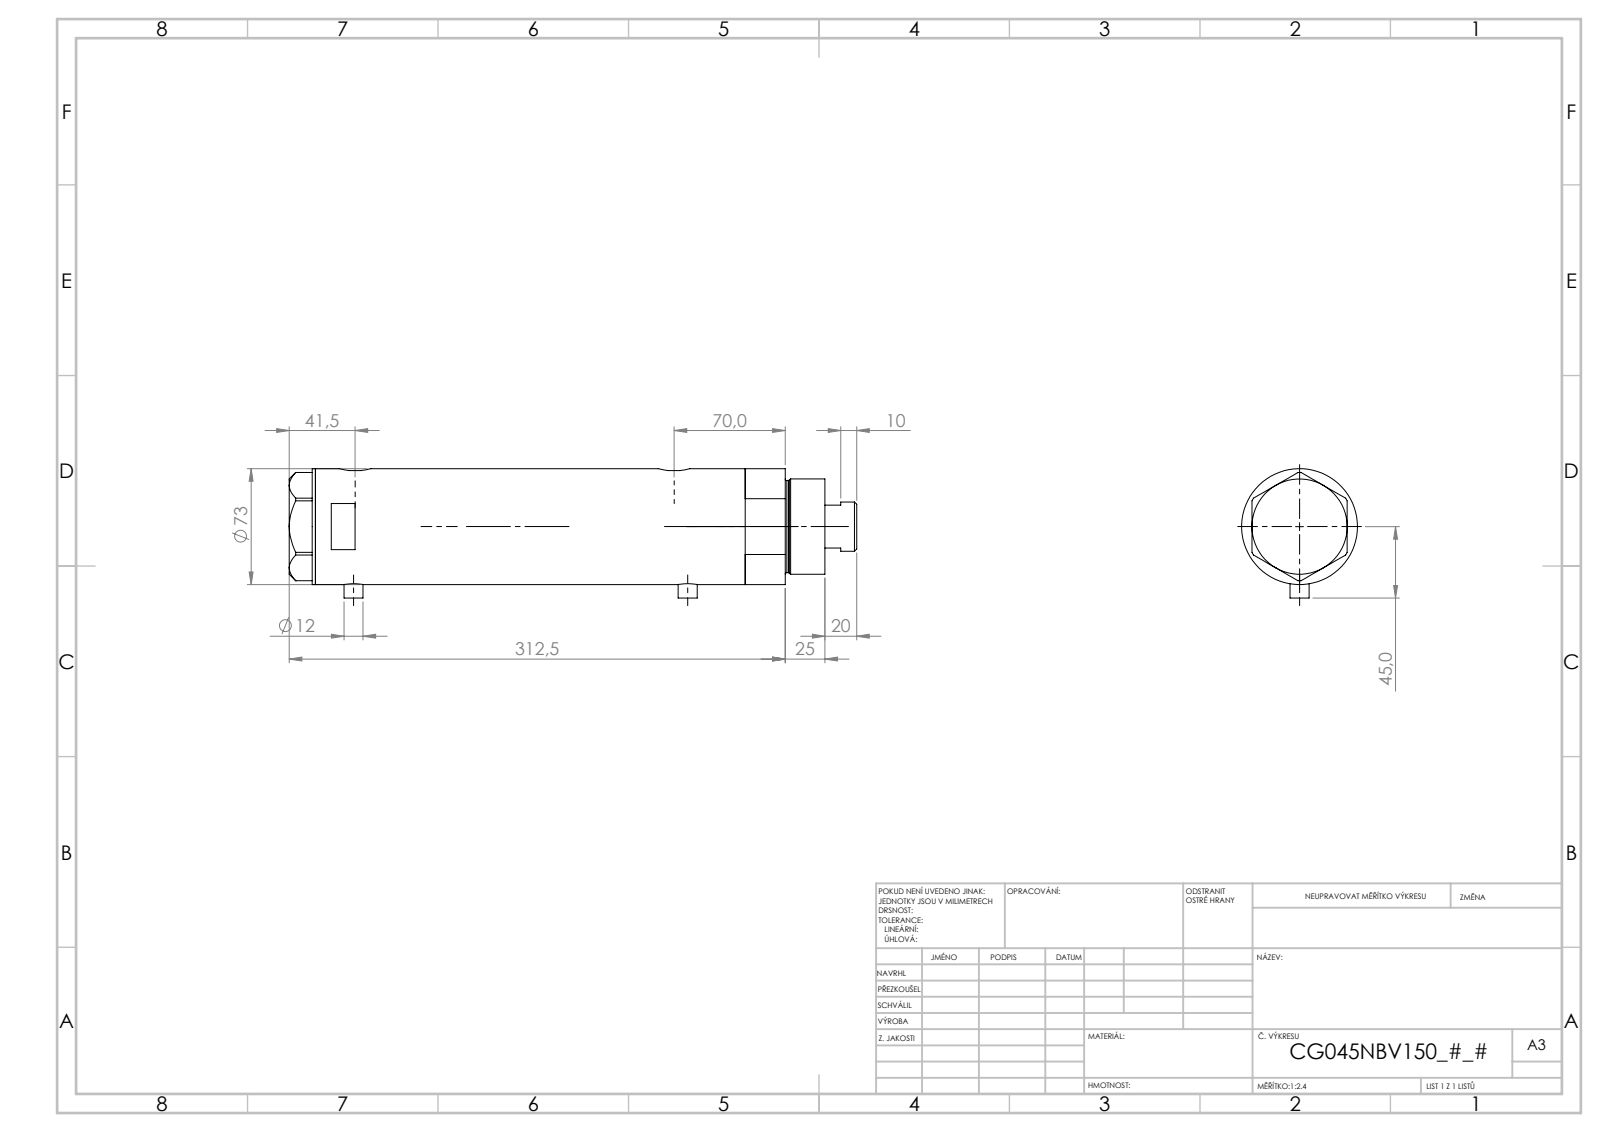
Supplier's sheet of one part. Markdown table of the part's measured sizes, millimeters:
| quantity | value |
| --- | --- |
| part name | V270CG_BACK; V270CG_VC; V270CG_FRONT; V270CG_MIDDLE |
| STEP written by | SolidWorks 2019 (CONFIG_CONTROL_DESIGN) |
| units | millimeters |
| bodies | 4 solids, 120 faces (49 planar, 51 cylindrical, 20 other) |
| overall size | 357.5 × 81.5 × 73 |
| volume | 1 247 000 mm³ |
| surface area | 198 635 mm² |
| round holes (diameter × count) | 12.5 × 2, 13.16 × 2, 10.5 × 1, 32 × 1, 33.5 × 1, 45 × 1, 48 × 1, 64 × 1 |
| round bosses / shafts (diameter × count) | 12 × 2, 73 × 1, 60 × 1, 58 × 1, 31 × 1 |
| partial cylindrical surfaces (radius × count) | 10 × 2 |
| main face-to-face distances | 226, 26, 200, 16.5, 42.5, 242.5, 2, 321, 337.5, 295 |
| hole center spacings | 1, 8.5, 201, 202, 209.5, 210.5 |
